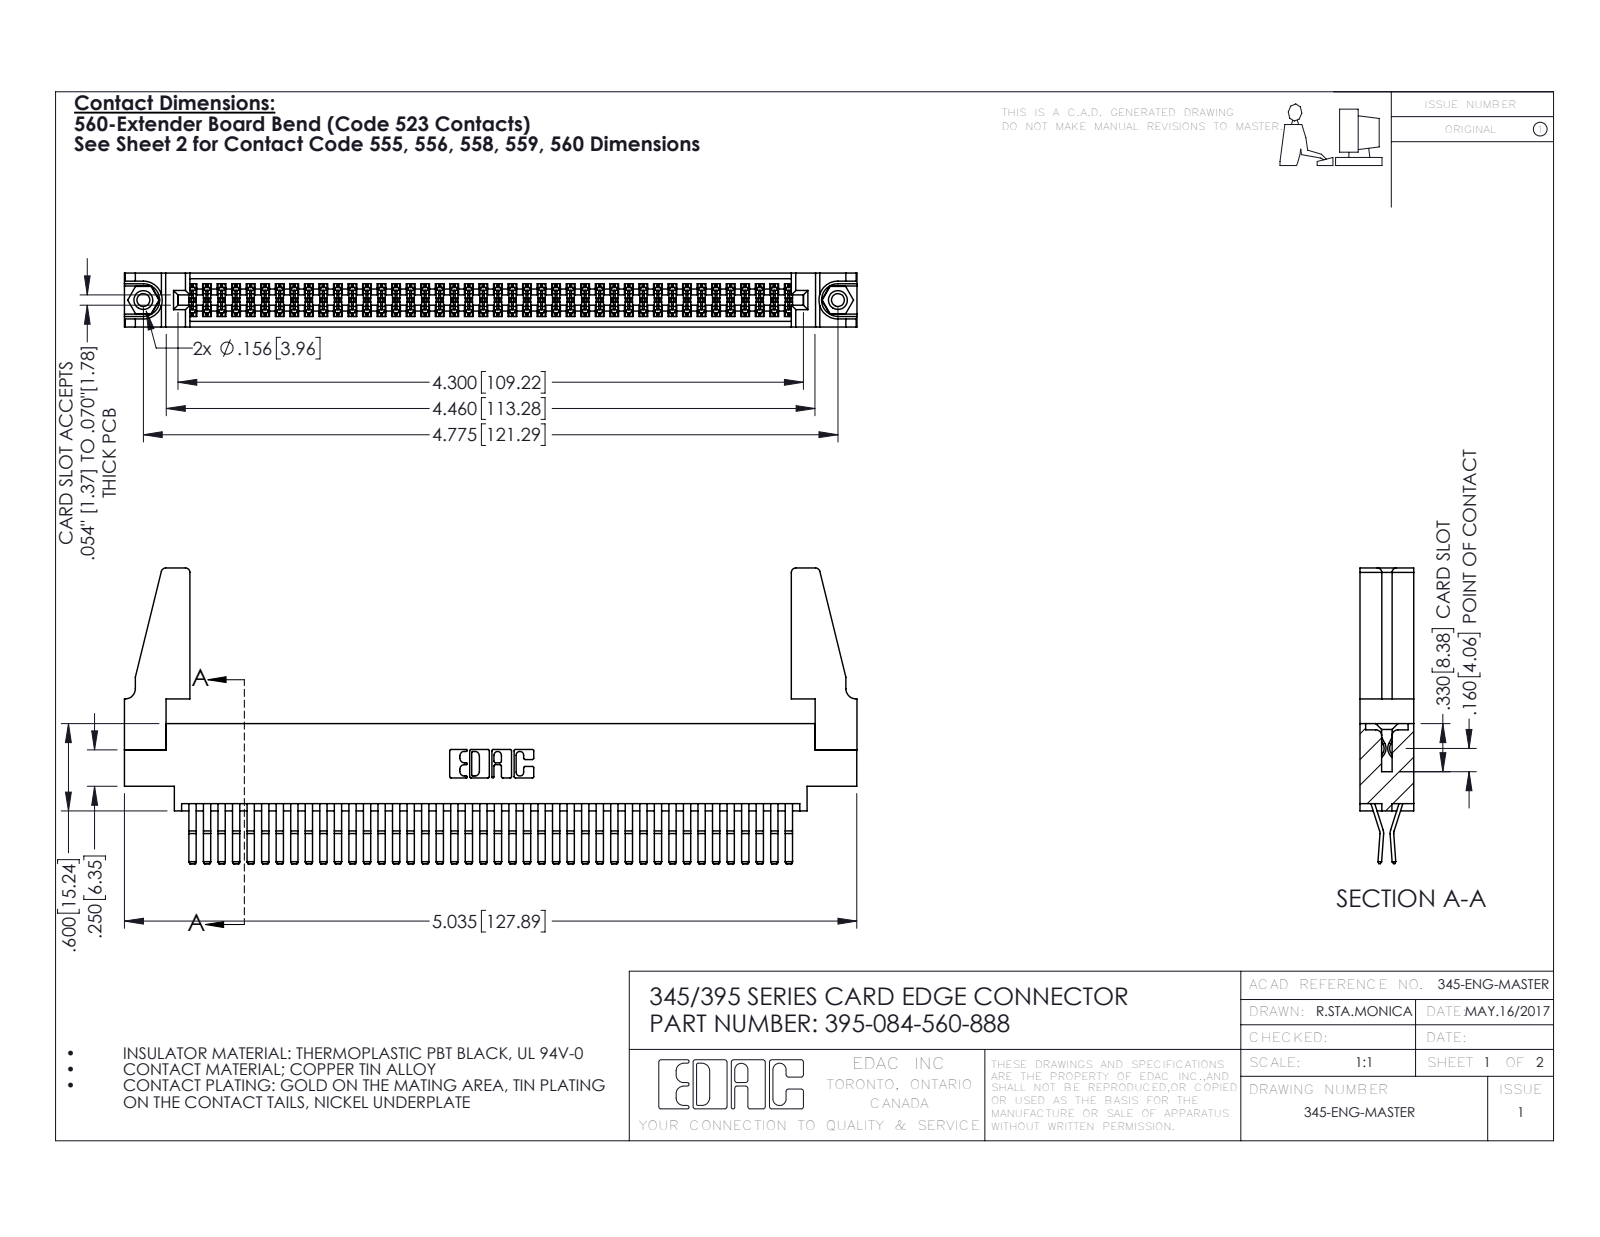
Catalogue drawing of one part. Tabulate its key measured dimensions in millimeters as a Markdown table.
| quantity | value |
| --- | --- |
| part name | 395-084-560-888; 345-220-078_345-220-088; 345 Part_0.170 Offset - 0.156 Dia-TH; 345-250-001_345-250-001-102 (+1 more) |
| STEP written by | SolidWorks 2016 (CONFIG_CONTROL_DESIGN) |
| units | millimeters |
| bodies | 89 solids, 4622 faces (2928 planar, 1678 cylindrical, 16 other) |
| overall size | 127.9 × 51.6 × 9.4 |
| volume | 16 100 mm³ |
| surface area | 23 700 mm² |
| round holes (diameter × count) | 2.3 × 2, 3.2 × 2, 4 × 2, 1.6 × 1 |
| round bosses / shafts (diameter × count) | 3.9 × 2 |
| partial cylindrical surfaces (radius × count) | 0.2 × 127, 0.3 × 22, 0.8 × 8, 0.2 × 6, 0.8 × 6, 0.7 × 3, 0.3 × 2, 0.4 × 2 |
| main face-to-face distances | 1.8, 7.6, 0.6, 9.4, 5.1, 2.5, 6.9, 5.7, 4.4, 3.8 |
| hole center spacings | 6.9, 115.3, 121.3 |
